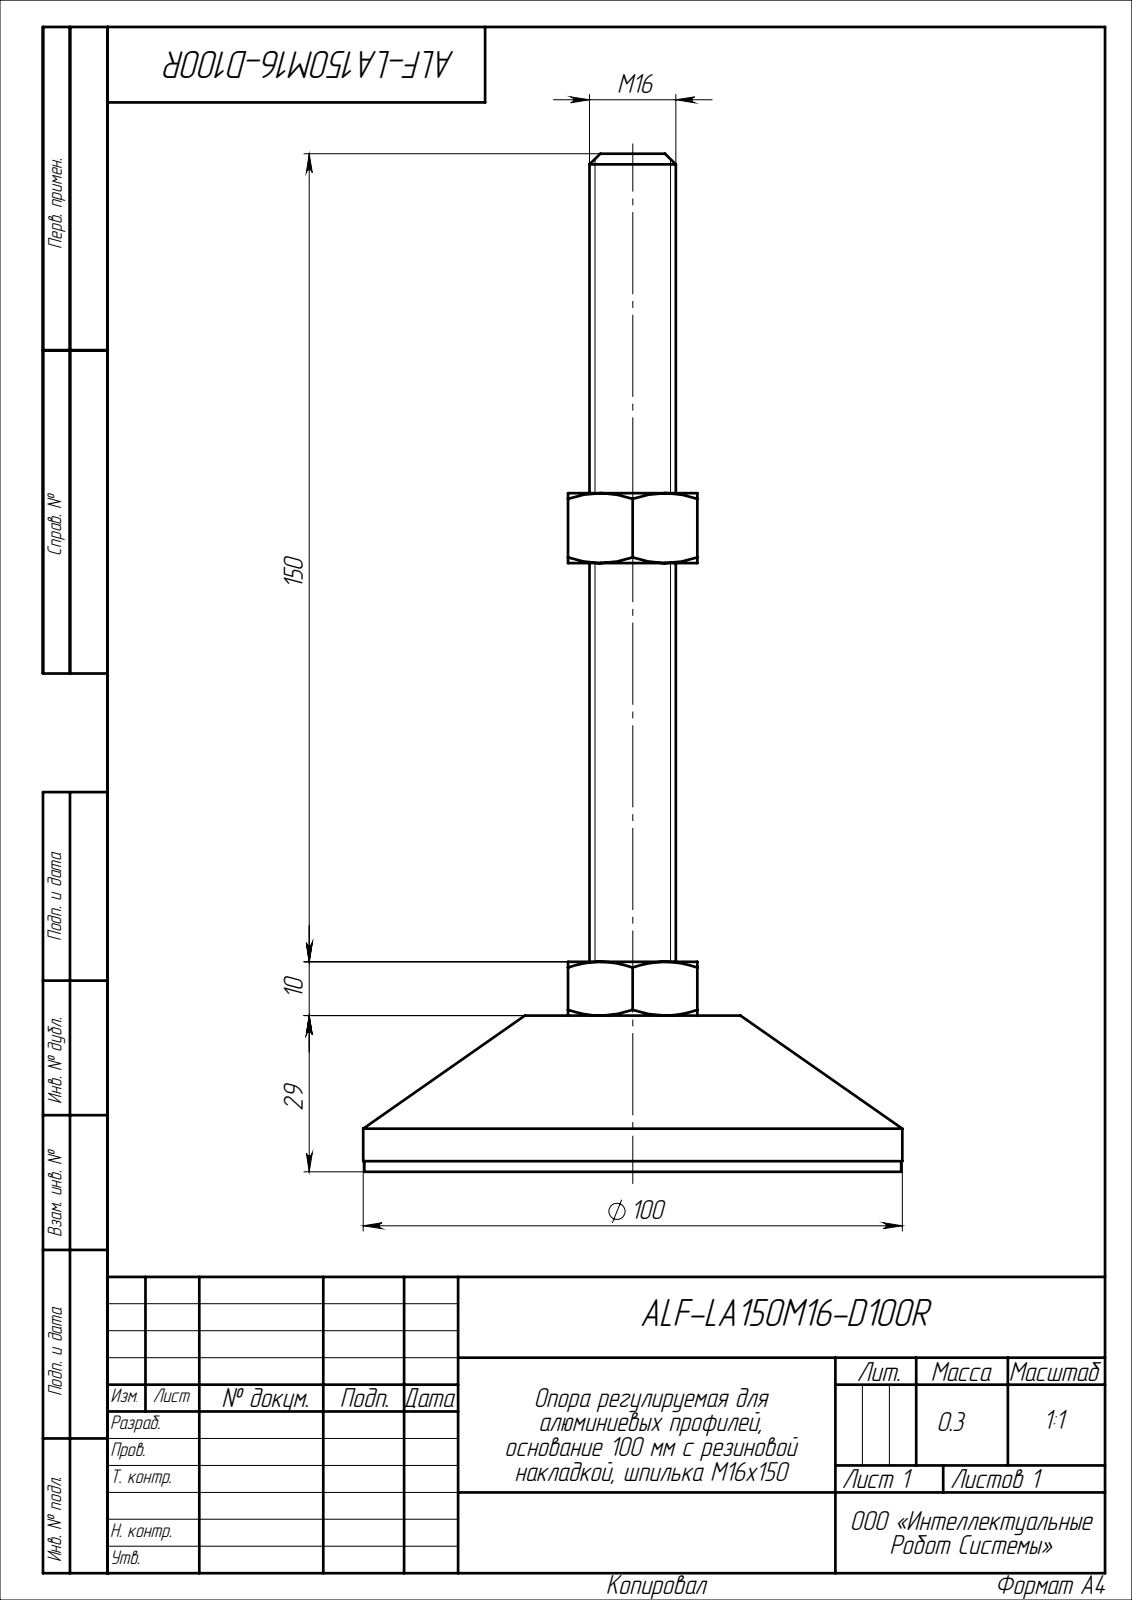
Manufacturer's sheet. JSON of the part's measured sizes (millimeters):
{"part_name": "ALF-LA150M16-D100R", "step_written_by": "SolidWorks 2022 (CONFIG_CONTROL_DESIGN)", "units": "millimeters", "bodies": {"solids": 1, "faces": 55, "planar": 19, "cylindrical": 8, "other": 28}, "overall_size": [189, 100, 100], "volume_mm3": 187338, "surface_area_mm2": 29004, "round_bosses_or_shafts": [[100, 1], [99.6, 1], [16, 1]], "face_to_face_distances": [24, 29, 39, 10, 113, 84, 74, 126, 97, 87]}
